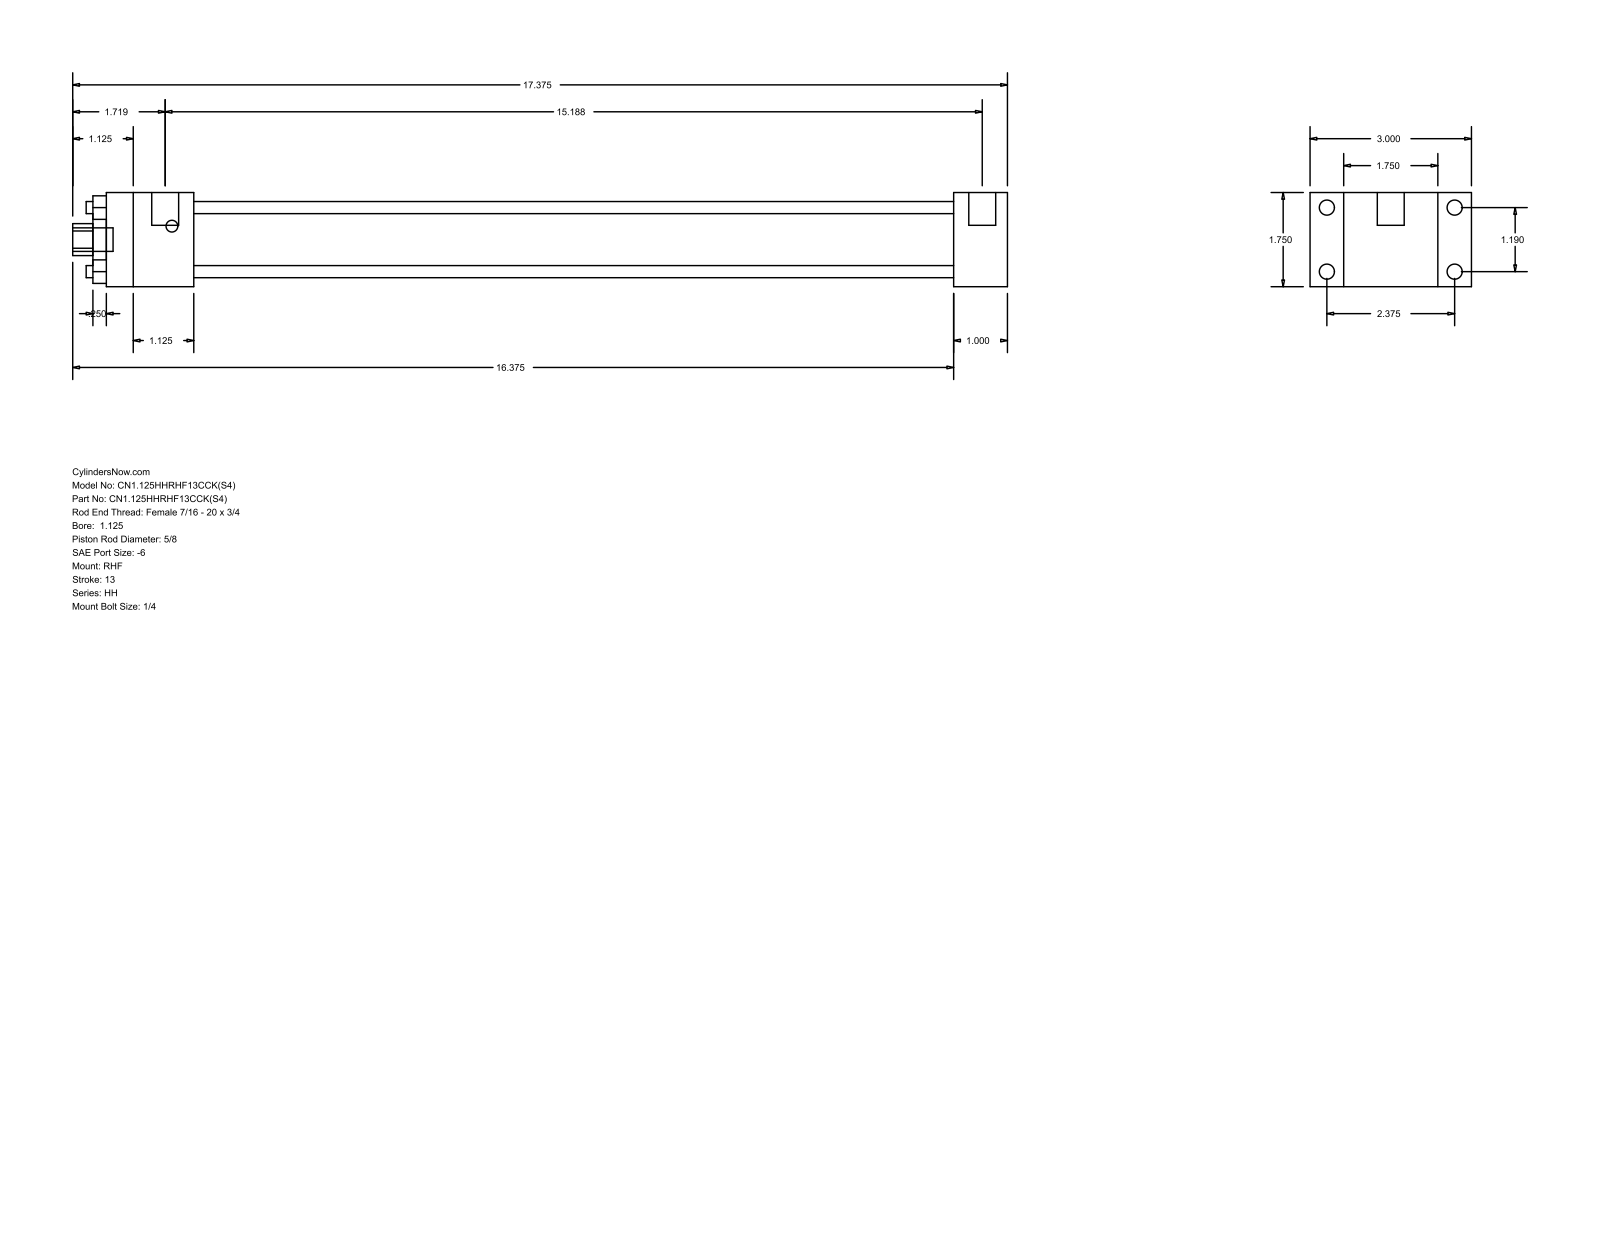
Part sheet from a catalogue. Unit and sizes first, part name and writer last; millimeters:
Units: millimetres
Overall size (bounding box): 441.32 × 76.2 × 44.45
Round holes (diameter × count): ⌀5.71 ×4, ⌀15.88 ×1, ⌀28.57 ×1, ⌀34.92 ×1
Round bosses / shafts (diameter × count): ⌀7.14 ×4, ⌀5.56 ×4, ⌀12.7 ×2, ⌀11.11 ×1
Partial cylindrical surfaces — rounded edges, fillets, slot ends (radius × count): R7.54 ×1
Main face-to-face distances: 44.46, 15.87, 60.33, 25.39, 76.2, 358.78, 384.17, 41.27, 400.05, 425.44
Hole centre spacings: 21.37, 30.22, 42.74
Bodies: 0 solids, 88 faces (60 planar, 28 cylindrical, 0 other)
Part name (STEP PRODUCT): HH_RHF__0112_0.625
STEP written by: GSSL Pune (CONFIG_CONTROL_DESIGN)
